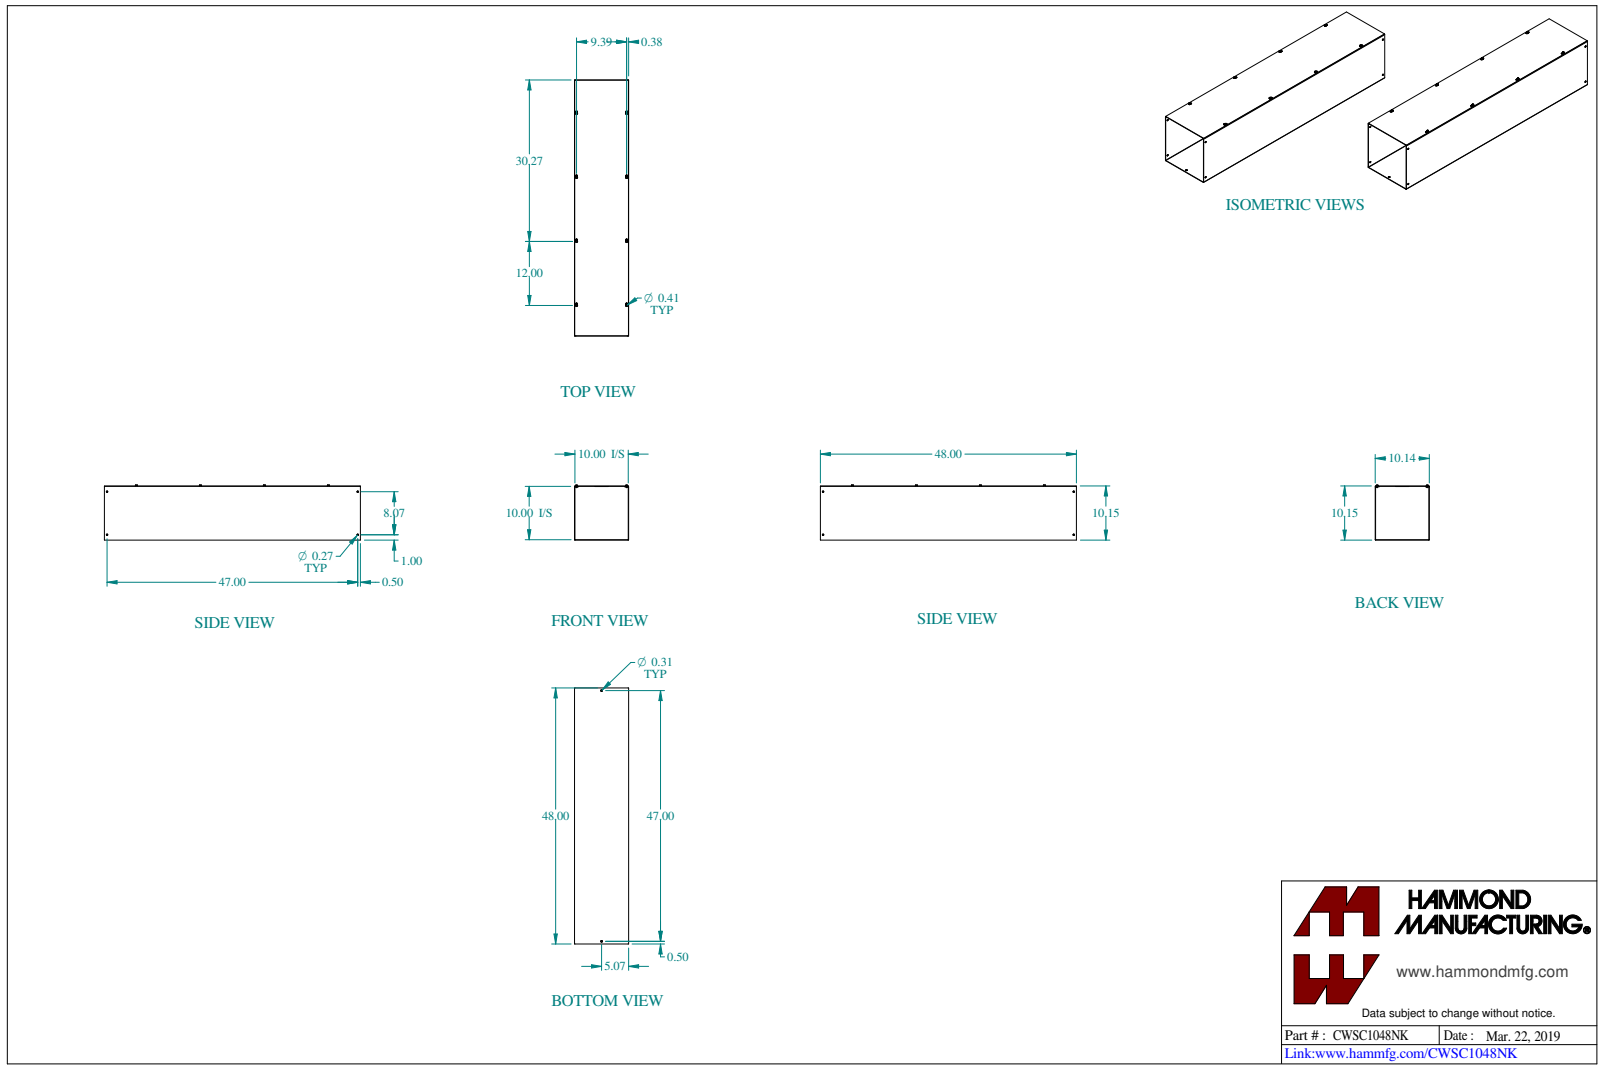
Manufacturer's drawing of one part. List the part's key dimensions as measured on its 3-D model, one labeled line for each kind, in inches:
Part name (STEP PRODUCT): CWSC1048NK
STEP written by: SolidWorks 2023 (CONFIG_CONTROL_DESIGN)
Units: inches
Bodies: 10 solids, 304 faces (148 planar, 108 cylindrical, 48 other)
Overall size (bounding box): 48 × 10.325 × 10.144
Volume: 146 in³ · Surface area: 3 997 in²
Round holes (diameter × count): ⌀0.177 ×8, ⌀0.266 ×4, ⌀0.313 ×2
Round bosses / shafts (diameter × count): ⌀0.375 ×8, ⌀0.19 ×8
Partial cylindrical surfaces — rounded edges, fillets, slot ends (radius × count): R0.125 ×8, R0.203 ×8, R0.036 ×4, R0.108 ×4
Main face-to-face distances: 0.072, 10.072, 10, 0.078, 10.15, 10.078, 10.144, 9.928, 0.15, 0.031
Hole centre spacings: 12, 15.239, 7.233, 9.394, 18.119, 24, 25.773, 29.872
